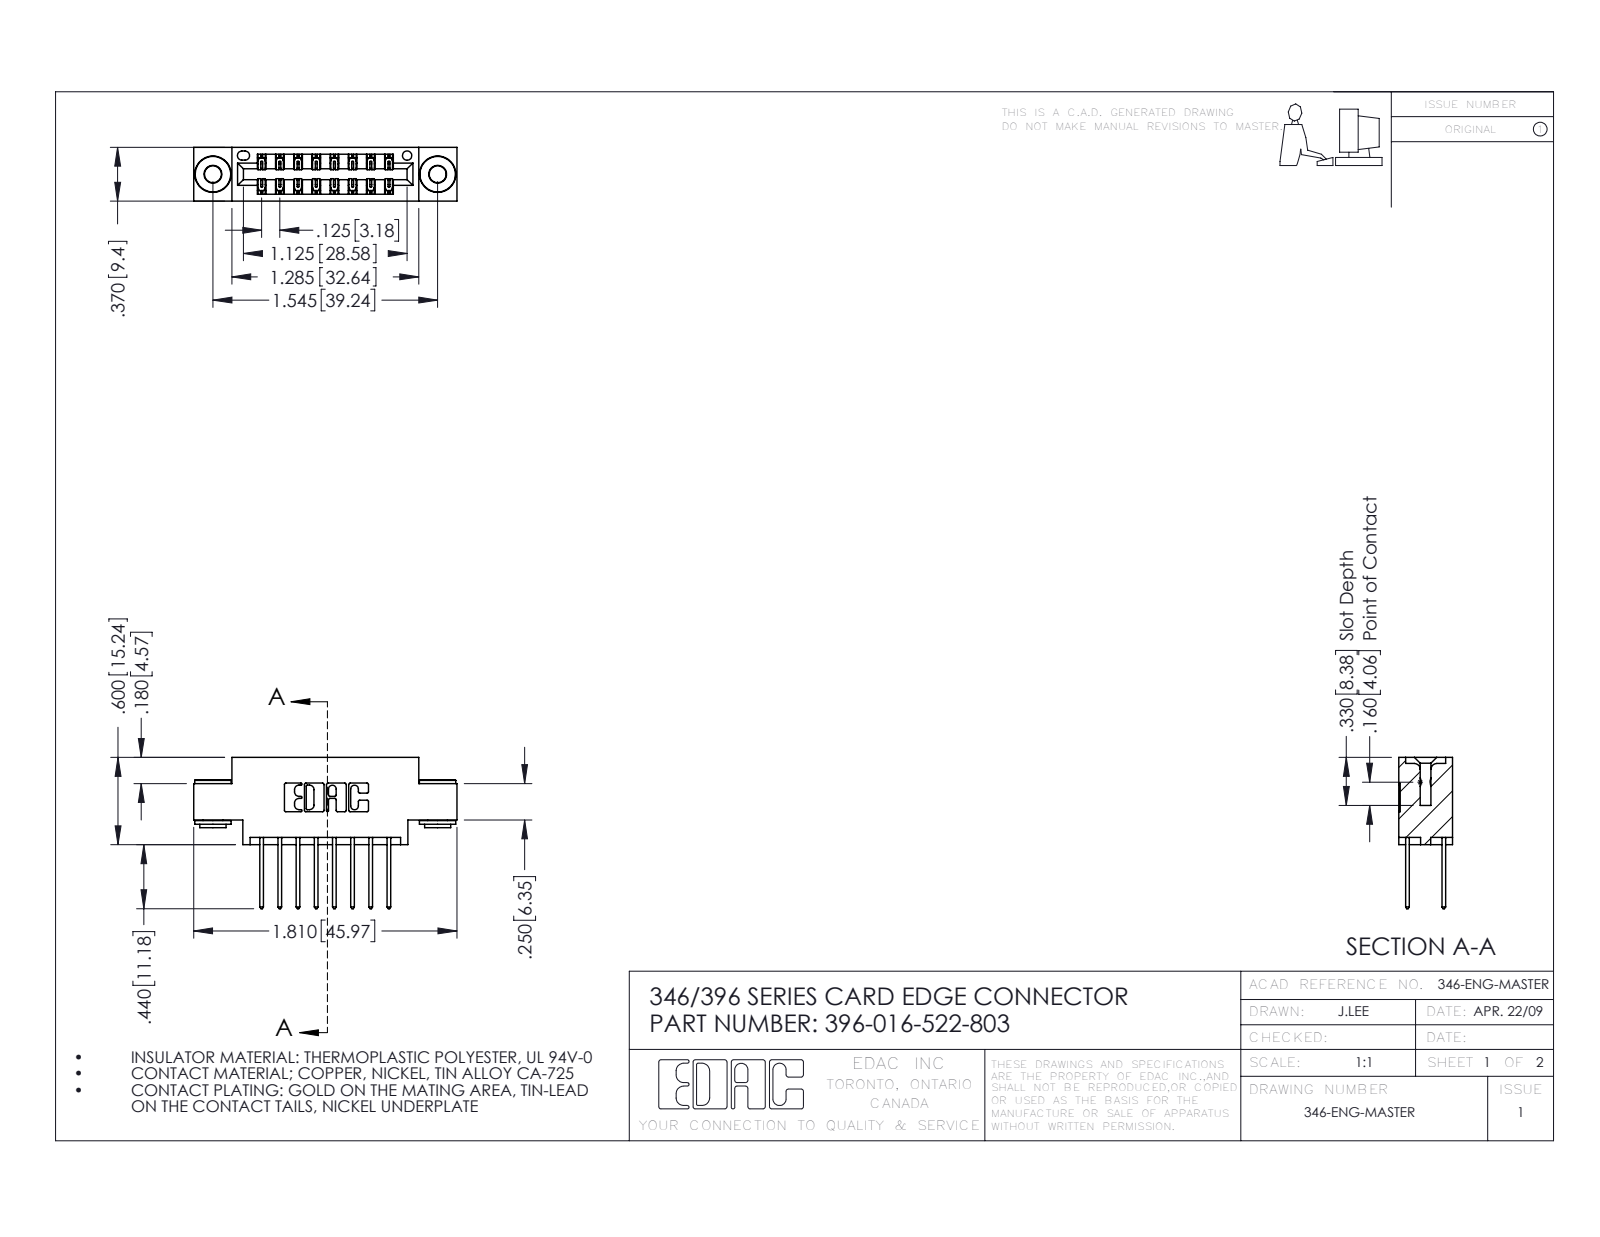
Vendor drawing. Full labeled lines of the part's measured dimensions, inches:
Part name (STEP PRODUCT): 396-016-522-803; 345-292-001_345-293-122; 345-250-002_345-250-002-102; 346 Part_0.170 Offset - 0.156 Dia-TH
STEP written by: SolidWorks 2016 (CONFIG_CONTROL_DESIGN)
Units: inches
Bodies: 19 solids, 996 faces (650 planar, 338 cylindrical, 8 other)
Overall size (bounding box): 1.81 × 1.04 × 0.37
Volume: 0.252 in³ · Surface area: 8.865 in²
Round holes (diameter × count): ⌀0.116 ×2, ⌀0.156 ×2, ⌀0.064 ×1
Round bosses / shafts (diameter × count): ⌀0.25 ×2, ⌀0.18 ×2, ⌀0.136 ×2
Partial cylindrical surfaces — rounded edges, fillets, slot ends (radius × count): R0.006 ×24, R0.01 ×22, R0.01 ×16, R0.007 ×6, R0.031 ×6, R0.026 ×3, R0.014 ×2, R0.022 ×2
Main face-to-face distances: 0.25, 0.37, 0.048, 0.322, 0.025, 0.072, 0.298, 0.275, 0.148, 0.222
Hole centre spacings: 0.246, 1.341, 1.545
